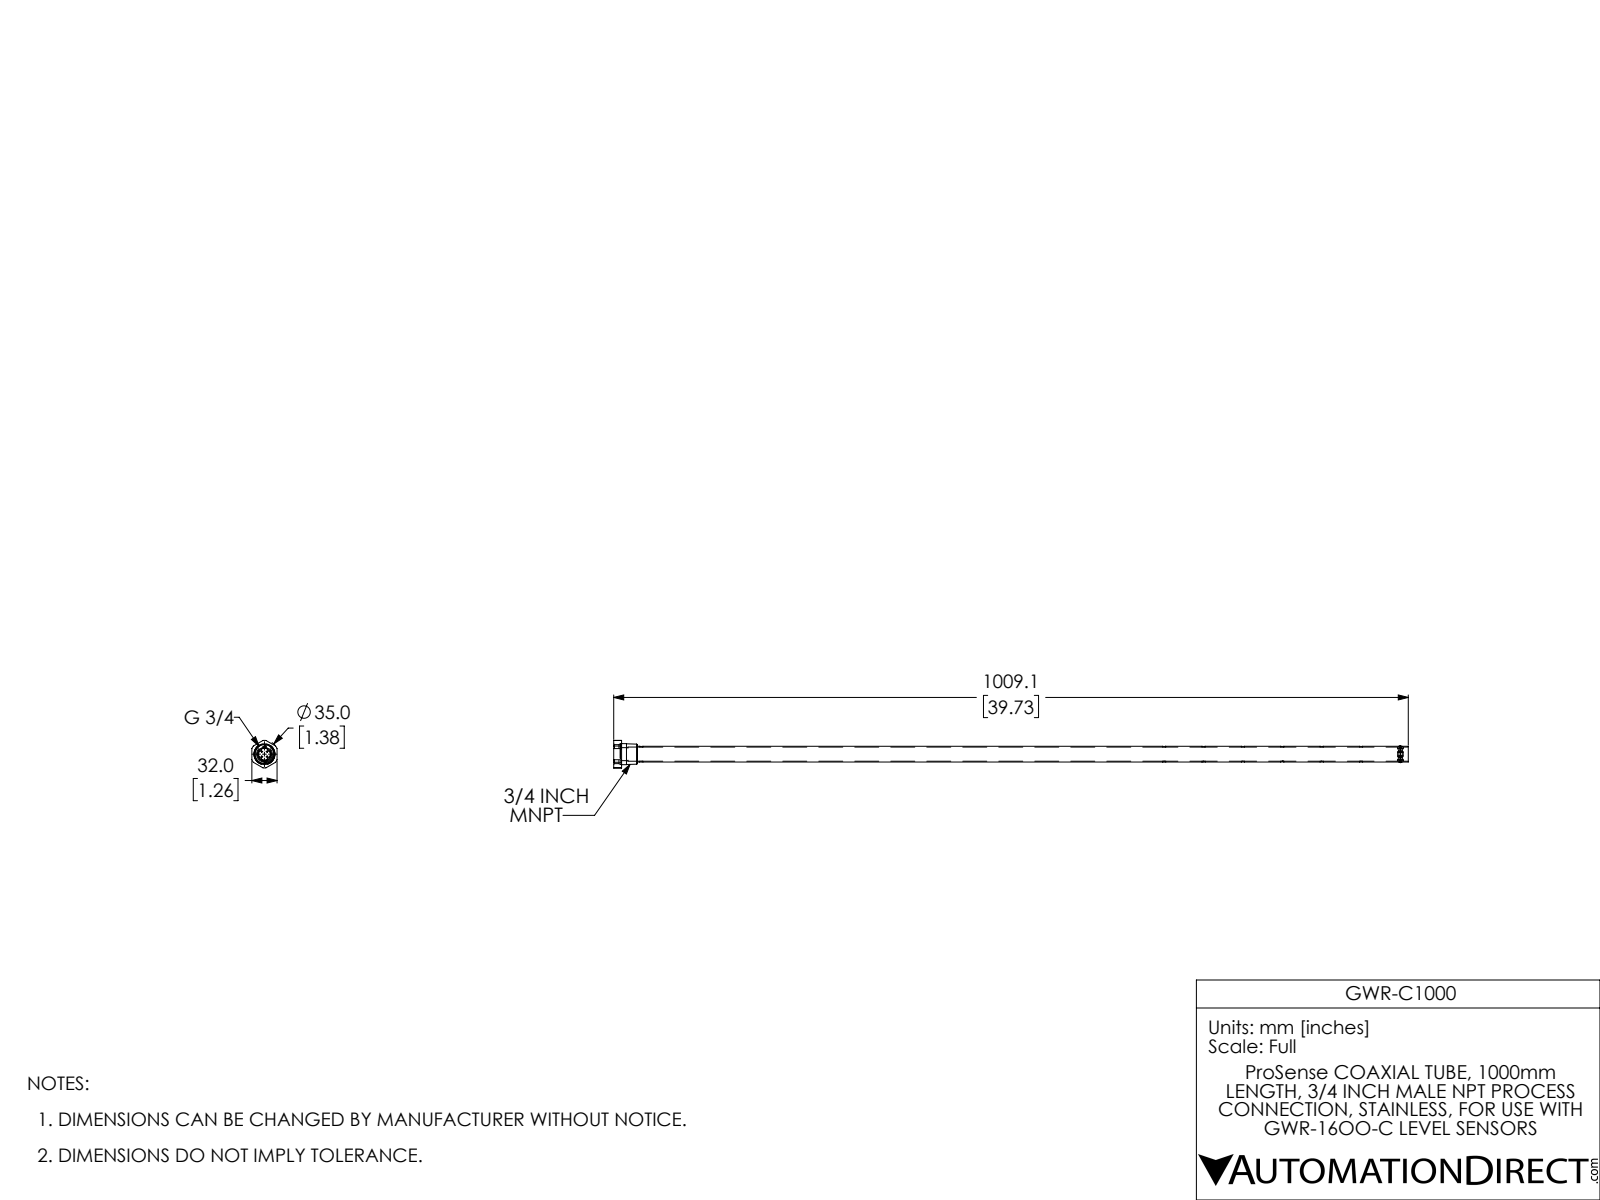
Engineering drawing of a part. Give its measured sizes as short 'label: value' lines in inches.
name: GWR-C1000
written by: SolidWorks 2017 (AUTOMOTIVE_DESIGN)
unit: in
bodies: 1 solid, 129 faces (19 planar, 88 cylindrical, 22 other)
size: 39.728 × 1.378 × 1.26
volume: 4.207 in³; area: 190.7 in²
holes: 8× ⌀0.157, 1× ⌀0.65, 1× ⌀0.709, 1× ⌀0.95
bosses: 1× ⌀1.053, 1× ⌀0.787
rounds: 8× R0.075, 1× R0.159, 1× R0.276, 1× R0.295, 1× R0.689
face distances: 1.26, 0.394, 0.035, 0.358, 0.787, 0.823, 1.181, 38.176, 38.963, 38.999
hole spacings: 1.969, 3.937, 5.906, 7.874, 9.843, 11.811, 26.142, 28.11
